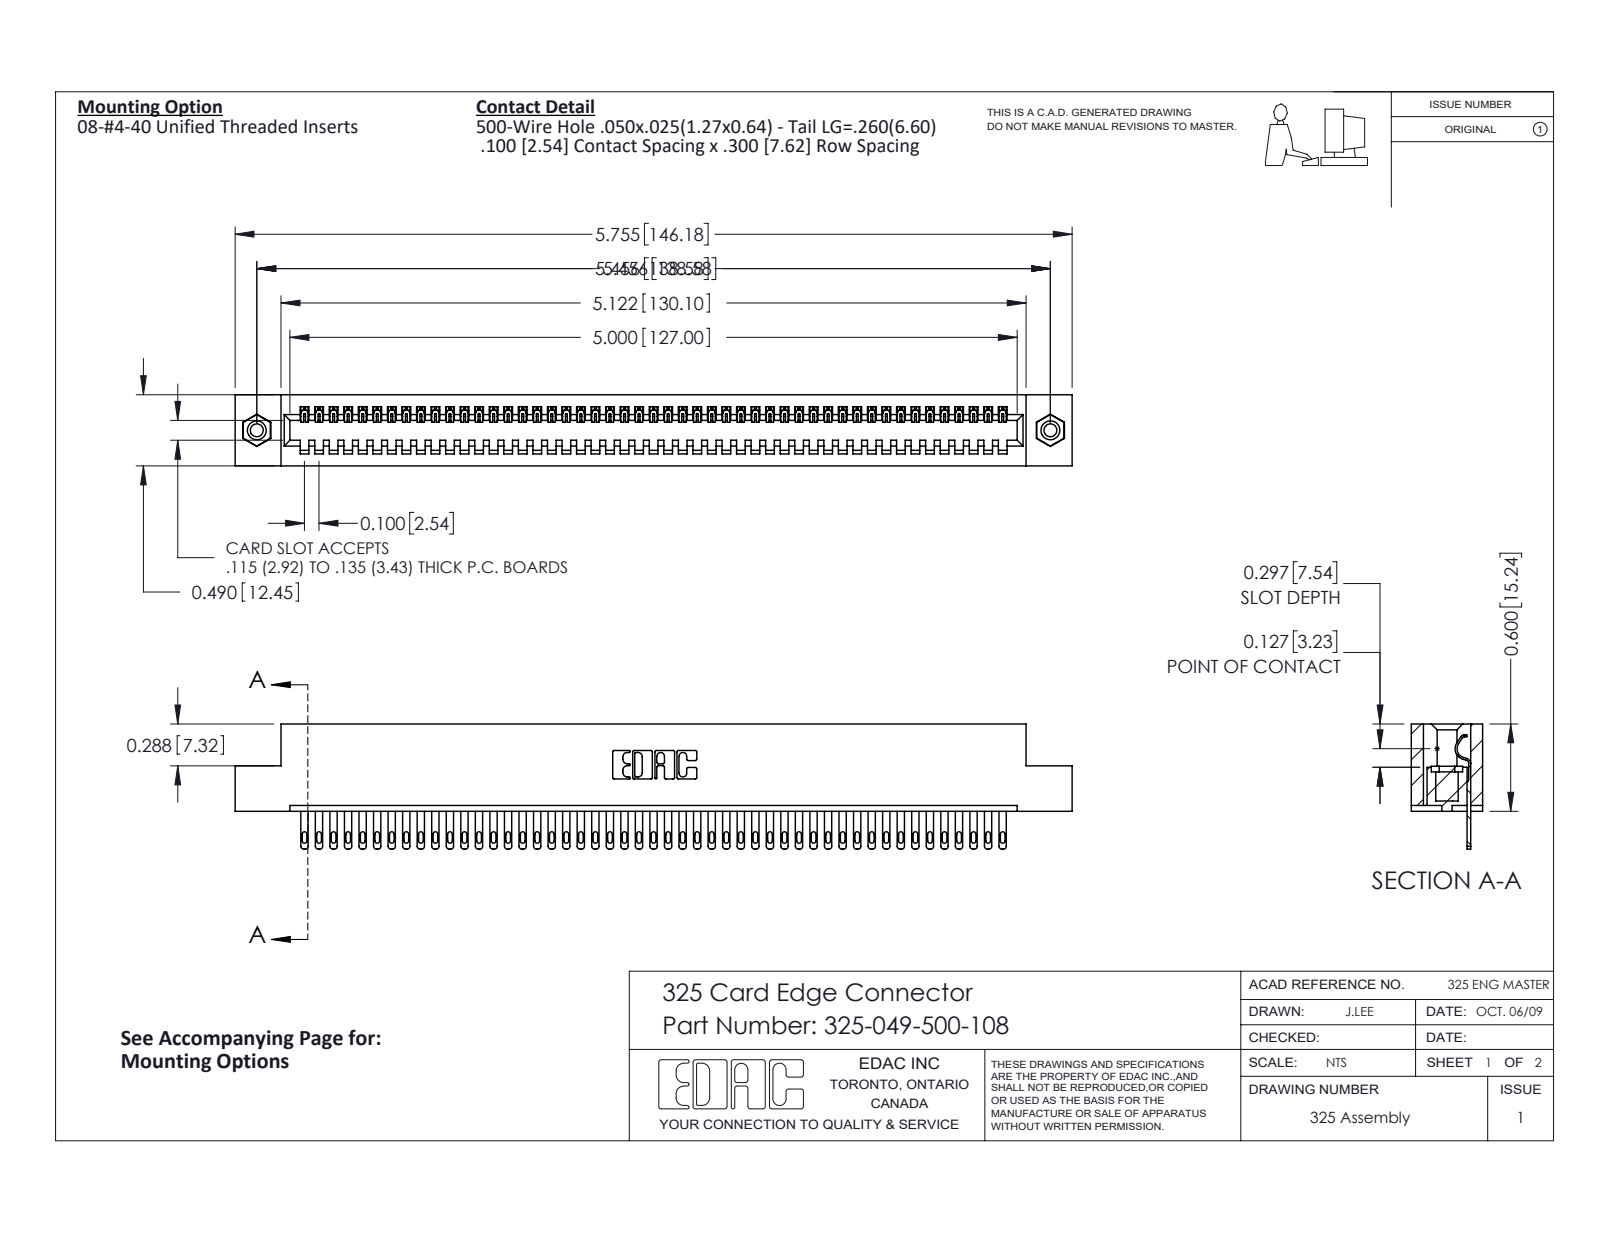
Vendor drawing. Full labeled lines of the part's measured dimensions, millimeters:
Part name (STEP PRODUCT): 345-250-001_345-250-003-102; 325-049-500-108; 325 Part_TI; 325-292-001_325-293-100
STEP written by: SolidWorks 2016 (CONFIG_CONTROL_DESIGN)
Units: millimetres
Bodies: 52 solids, 2820 faces (1866 planar, 938 cylindrical, 16 other)
Overall size (bounding box): 146.2 × 21.8 × 12.4
Volume: 18 630 mm³ · Surface area: 20 610 mm²
Round holes (diameter × count): ⌀2.3 ×2, ⌀3.2 ×2, ⌀4.1 ×2
Round bosses / shafts (diameter × count): ⌀3.9 ×2
Partial cylindrical surfaces — rounded edges, fillets, slot ends (radius × count): R0.2 ×98, R0.4 ×98, R0.5 ×98, R0.3 ×22, R0.2 ×6, R0.8 ×6, R0.7 ×3, R0.4 ×1
Main face-to-face distances: 2.1, 10.3, 12.4, 7.6, 2.7, 9.7, 0.6, 8.3, 14.2, 6.7
Hole centre spacings: 138.6
